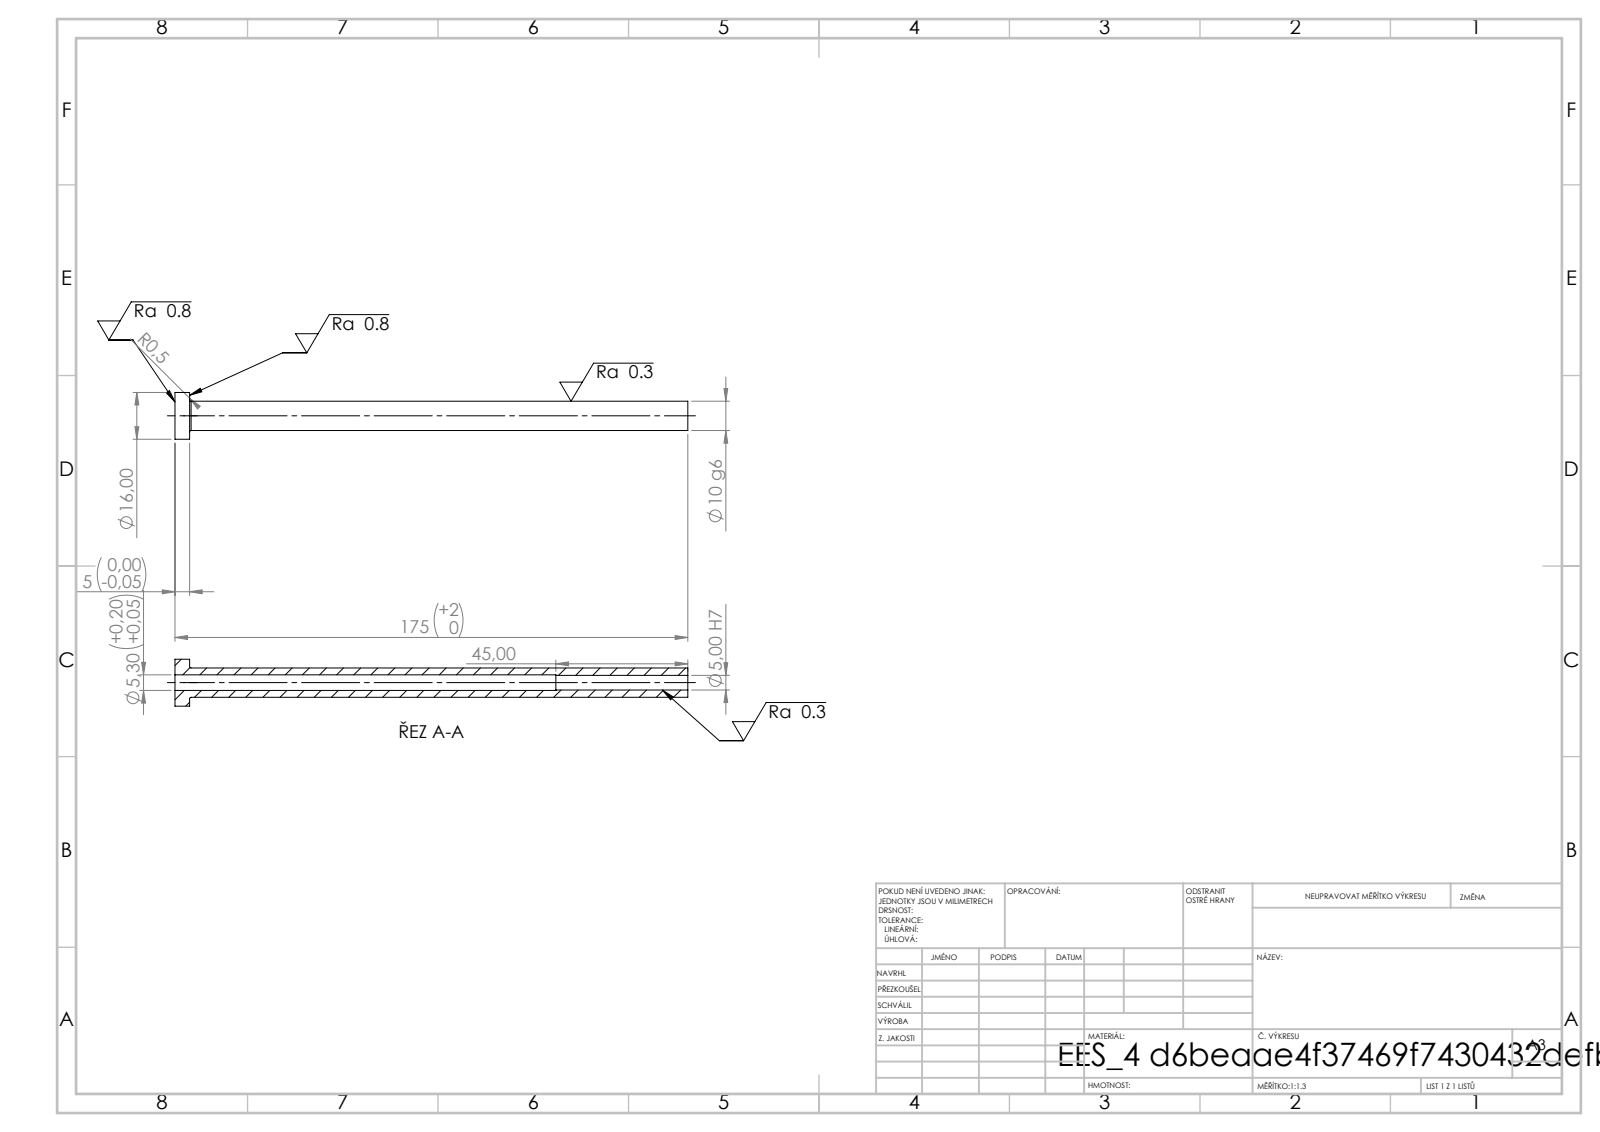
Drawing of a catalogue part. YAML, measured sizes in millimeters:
step_written_by: "SolidWorks 2019 (CONFIG_CONTROL_DESIGN)"
units: millimeters
bodies: {solids: 1, faces: 14, planar: 4, cylindrical: 8, other: 2}
overall_size: [175, 16, 16]
volume: 10607
surface_area: 8820
round_holes:
  - {diameter: 5, count: 1}
  - {diameter: 5.3, count: 1}
round_bosses_or_shafts:
  - {diameter: 16, count: 1}
  - {diameter: 10, count: 1}
face_to_face_distances: [5, 175, 170, 130, 125, 45]
